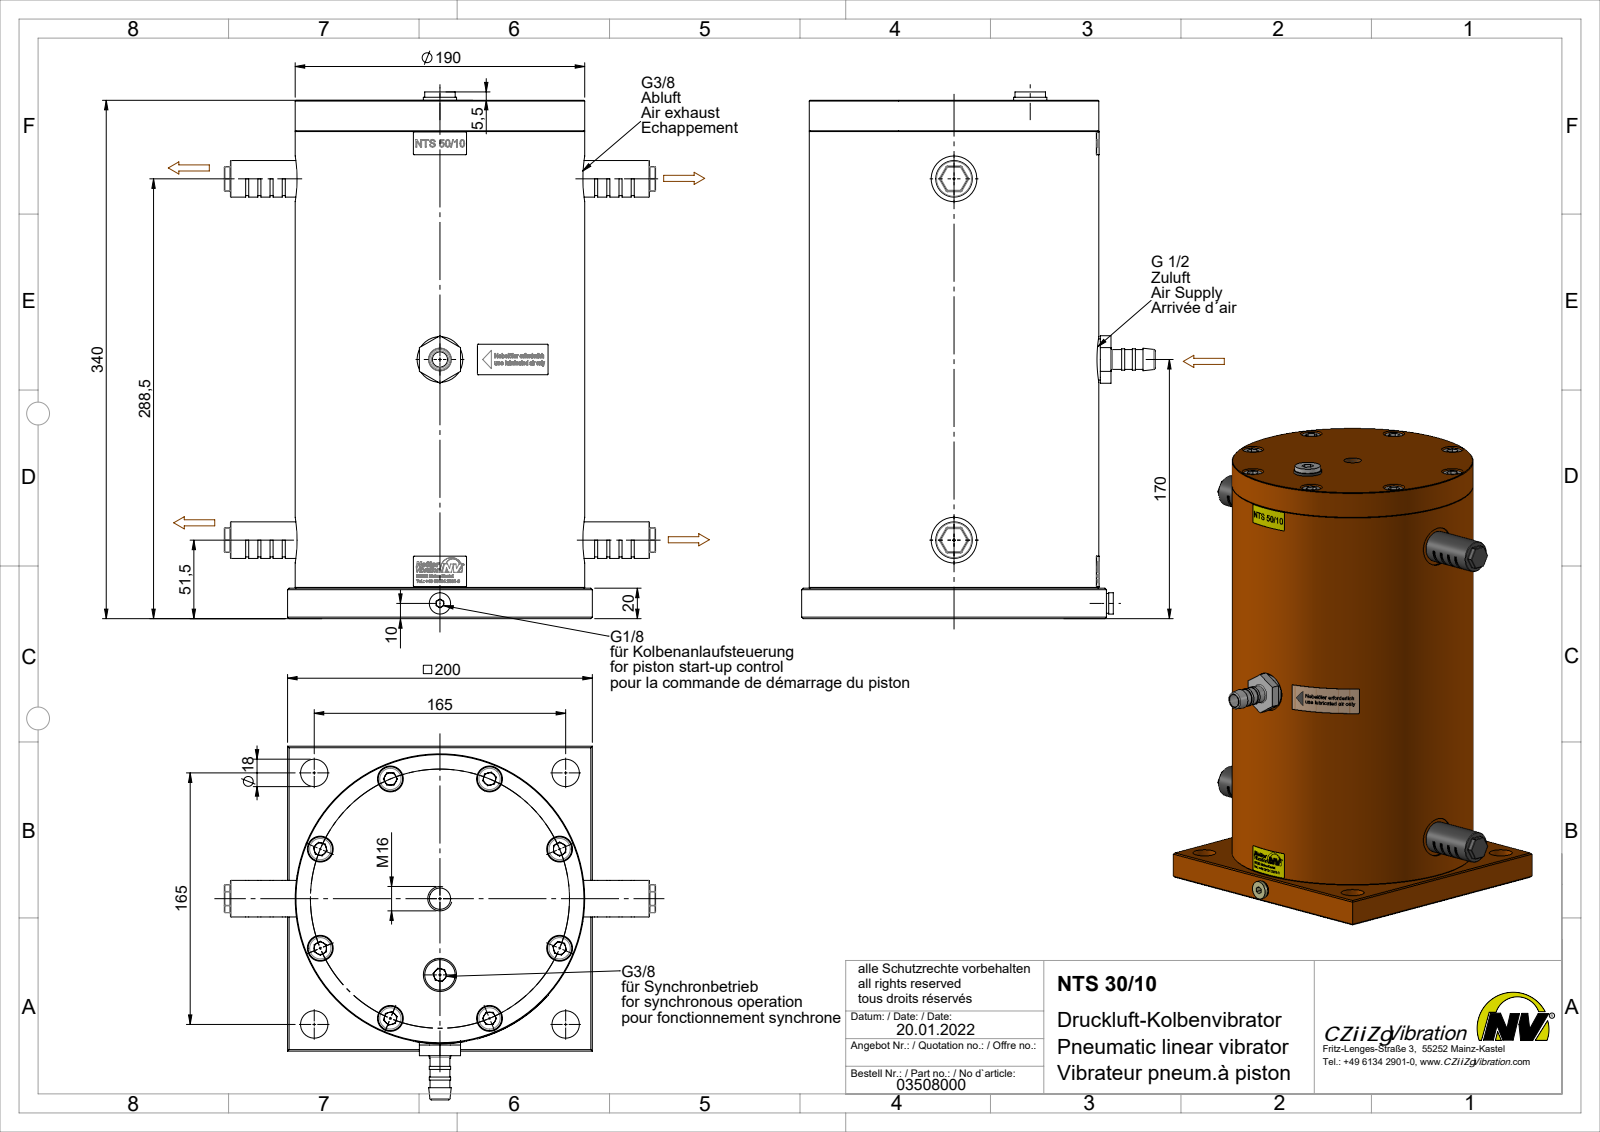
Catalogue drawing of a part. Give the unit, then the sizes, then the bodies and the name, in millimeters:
Units: millimetres
Overall size (bounding box): 345.5 × 283 × 232
Round holes (diameter × count): ⌀8.5 ×8, ⌀10.5 ×8, ⌀11 ×8, ⌀17 ×8, ⌀18 ×4, ⌀14.95 ×3, ⌀30 ×3, ⌀10 ×2, ⌀12 ×2, ⌀5 ×1, ⌀6 ×1, ⌀8.57 ×1
Round bosses / shafts (diameter × count): ⌀16 ×8, ⌀10 ×8, ⌀24 ×2, ⌀16.66 ×2, ⌀14 ×2, ⌀13 ×2, ⌀190 ×1, ⌀27 ×1
Partial cylindrical surfaces — rounded edges, fillets, slot ends (radius × count): R0.5 ×68, R11 ×2, R95.2 ×1
Main face-to-face distances: 300, 20, 320, 19, 1, 339, 319, 340, 200, 11
Hole centre spacings: 50.13, 85, 115.1, 120.21, 157.06, 168.61, 197.9, 65.05
Volume: 9 882 000 mm³ · Surface area: 501 711 mm²
Bodies: 30 solids, 1238 faces (443 planar, 477 cylindrical, 318 other)
Part name (STEP PRODUCT): NTS 30-10 Kolbenvibrator #03508000
STEP written by: SolidWorks 2022 (AUTOMOTIVE_DESIGN)
